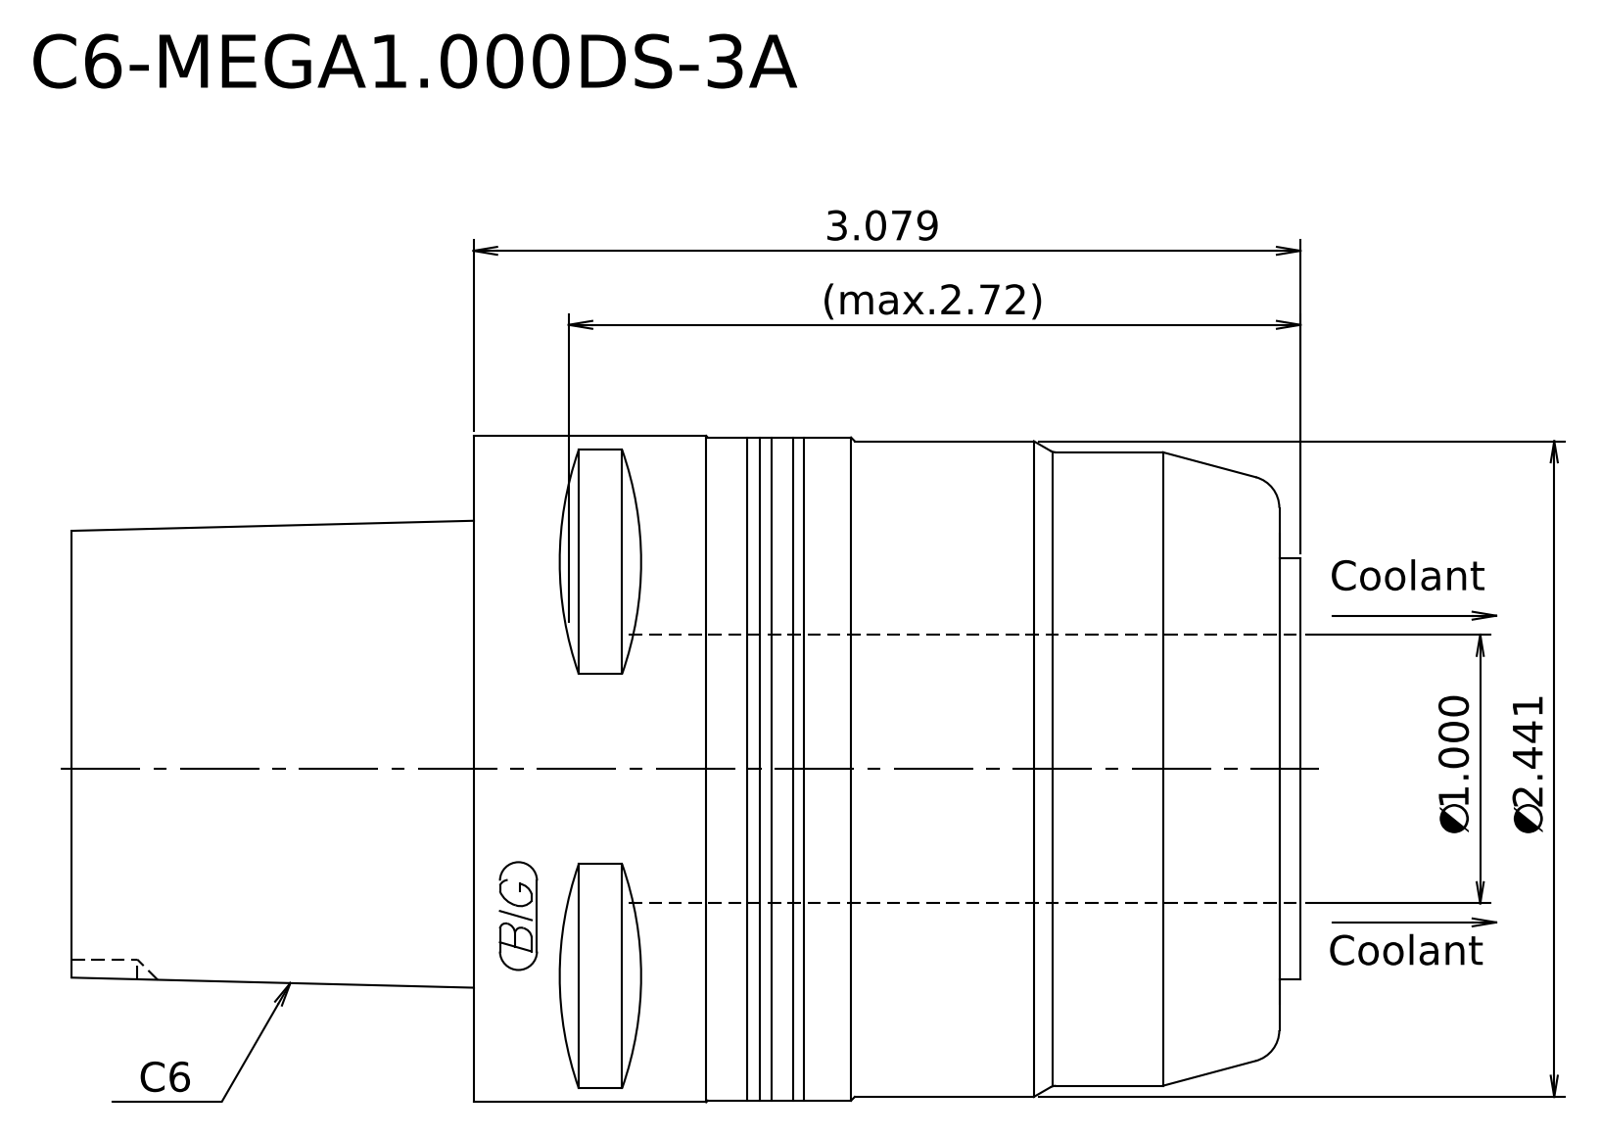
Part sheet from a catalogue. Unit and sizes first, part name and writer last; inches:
Units: inches
Overall size (bounding box): 4.575 × 2.48 × 2.48
Round bosses / shafts (diameter × count): ⌀2.48 ×1, ⌀2.469 ×1, ⌀2.441 ×1, ⌀2.358 ×1, ⌀1.569 ×1
Main face-to-face distances: 1.496, 3.079, 4.575, 0.079, 3, 4.496
Volume: 17.27 in³ · Surface area: 39.59 in²
Bodies: 1 solid, 16 faces (4 planar, 5 cylindrical, 7 other)
STEP written by: Kubotek KeyCreator 2011 V10.0.2 (22737) (automotive_design)
